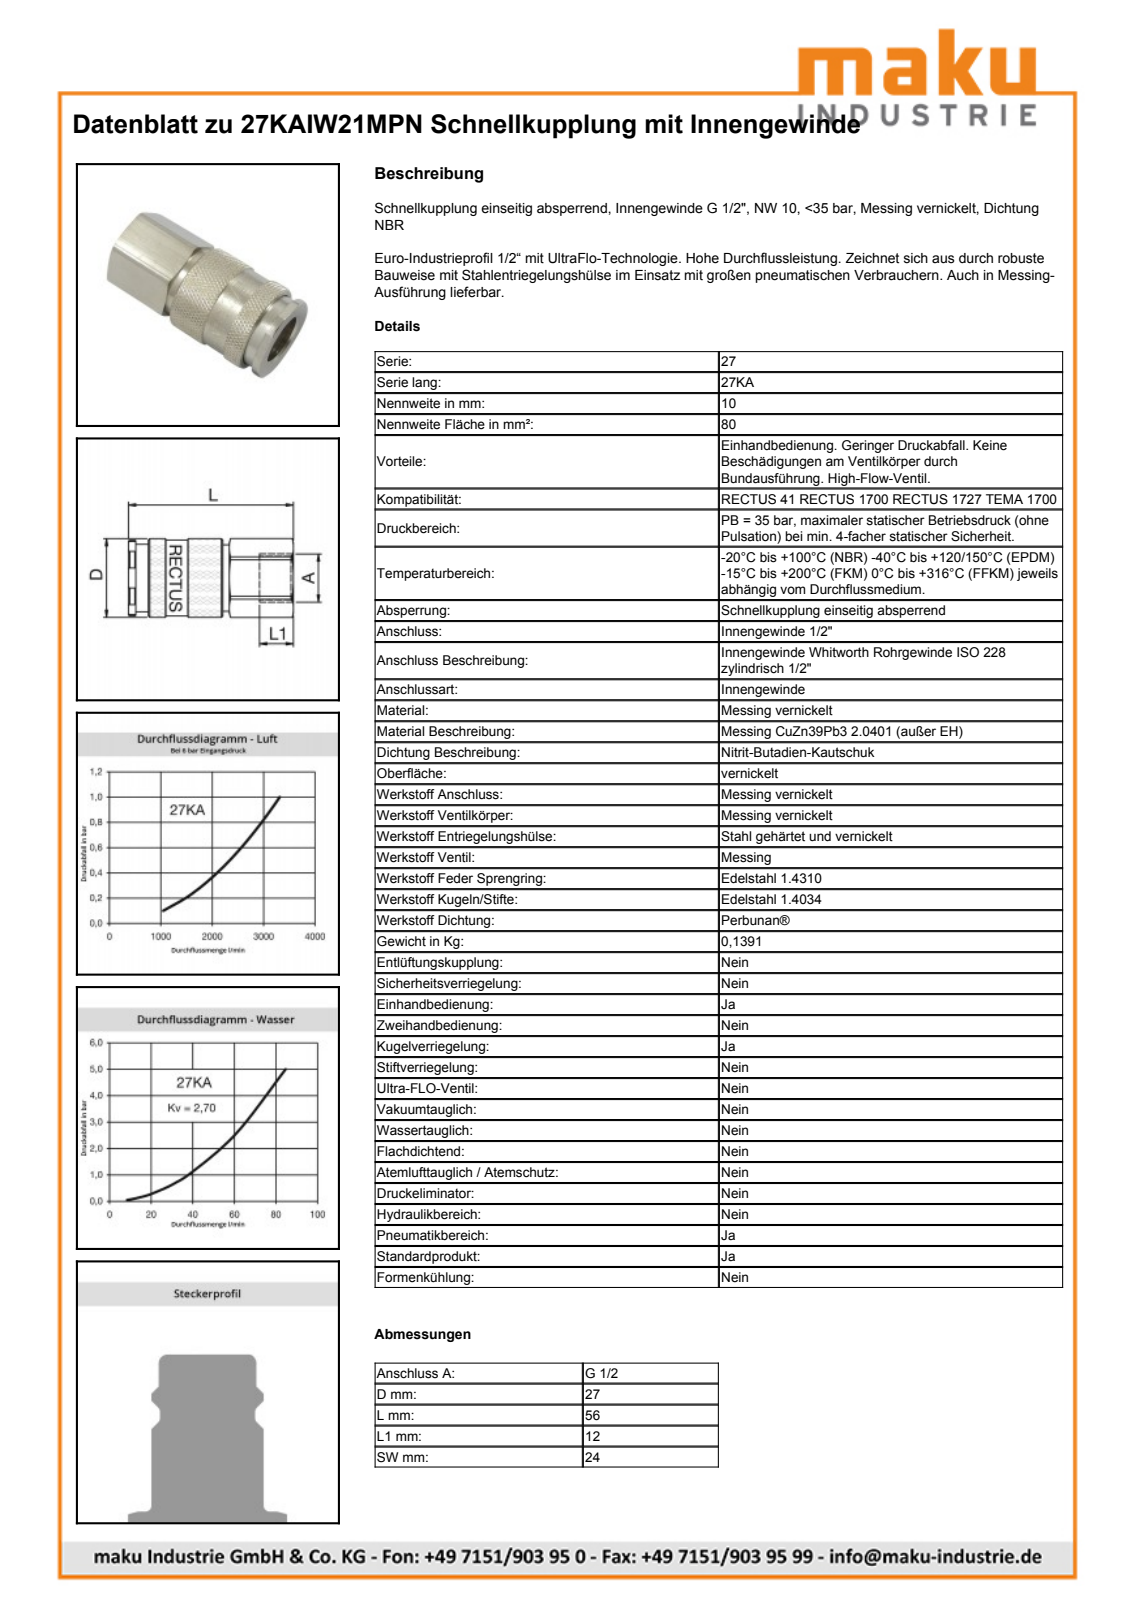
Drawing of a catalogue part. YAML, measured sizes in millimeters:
part_name: "D110652"
step_written_by: "Autodesk Inventor 2013 (AUTOMOTIVE_DESIGN)"
units: millimeters
bodies: {solids: 2, faces: 651, planar: 226, cylindrical: 79, other: 346}
overall_size: [56.45, 27.15, 27.15]
volume: 23993
surface_area: 10604
round_holes:
  - {diameter: 18.63, count: 1}
  - {diameter: 20.95, count: 1}
  - {diameter: 23.35, count: 1}
  - {diameter: 23.55, count: 1}
round_bosses_or_shafts:
  - {diameter: 27.15, count: 1}
  - {diameter: 26, count: 1}
  - {diameter: 23.1, count: 1}
  - {diameter: 22.75, count: 1}
  - {diameter: 20, count: 1}
partial_cylinders:
  - {radius: 9.74, count: 1}
  - {radius: 9.9, count: 1}
  - {radius: 12.9, count: 1}
  - {radius: 13.53, count: 1}
face_to_face_distances: [24, 44.45, 32.3, 12.15, 56.45, 24.15, 12, 6.8, 25.5, 37.65]
